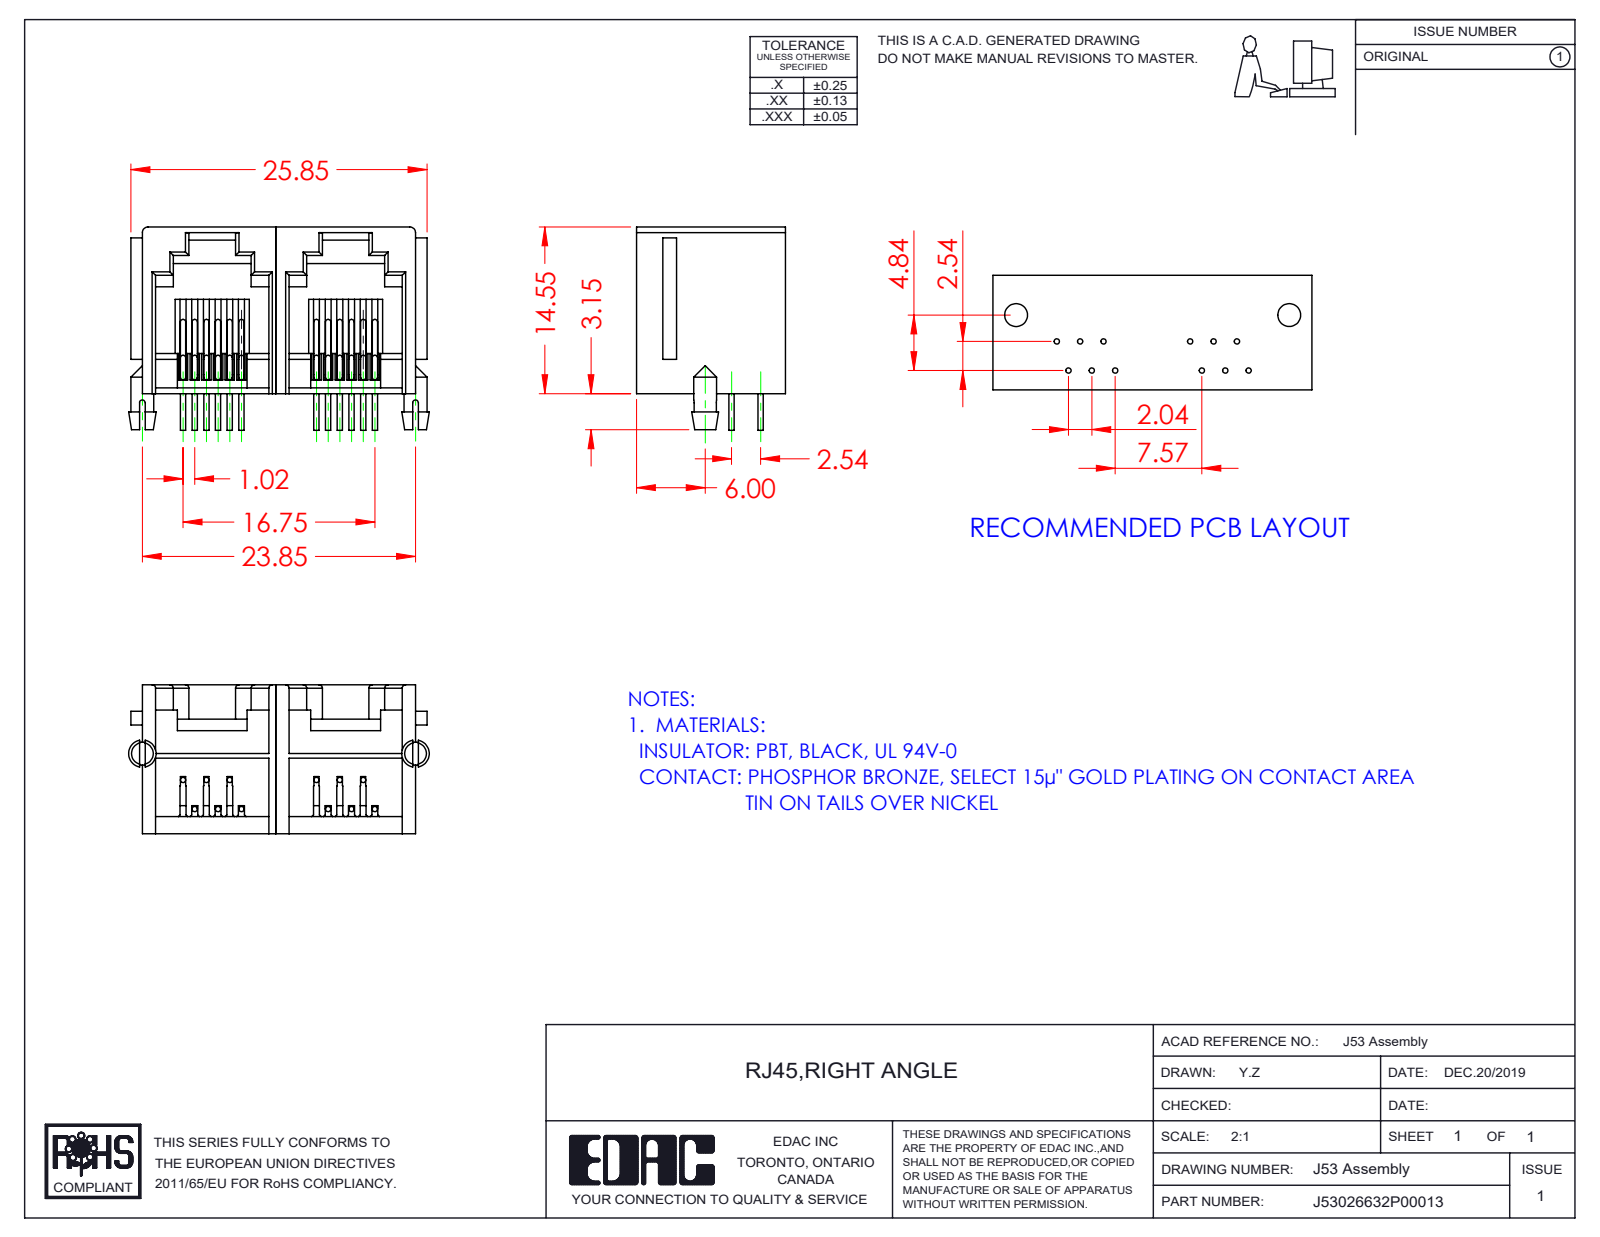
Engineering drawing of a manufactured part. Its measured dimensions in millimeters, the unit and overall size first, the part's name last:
Units: millimetres
Overall size (bounding box): 26.25 × 17.75 × 13
Round bosses / shafts (diameter × count): ⌀0.46 ×36, ⌀2 ×2
Partial cylindrical surfaces — rounded edges, fillets, slot ends (radius × count): R0.3 ×14, R0.5 ×10, R0.25 ×2, R0.67 ×1
Main face-to-face distances: 11.65, 1.16, 11.04, 12.2, 22.69, 10.49, 12.81, 0.61, 9.88, 3
Volume: 1 800 mm³ · Surface area: 4 280 mm²
Bodies: 14 solids, 595 faces (410 planar, 128 cylindrical, 57 other)
Part name (STEP PRODUCT): 53 Insulator LH; 53 Contacts; 53 Contact - 1; 53 Contact - 4 (+6 more)
STEP written by: SolidWorks 2016 (CONFIG_CONTROL_DESIGN)
